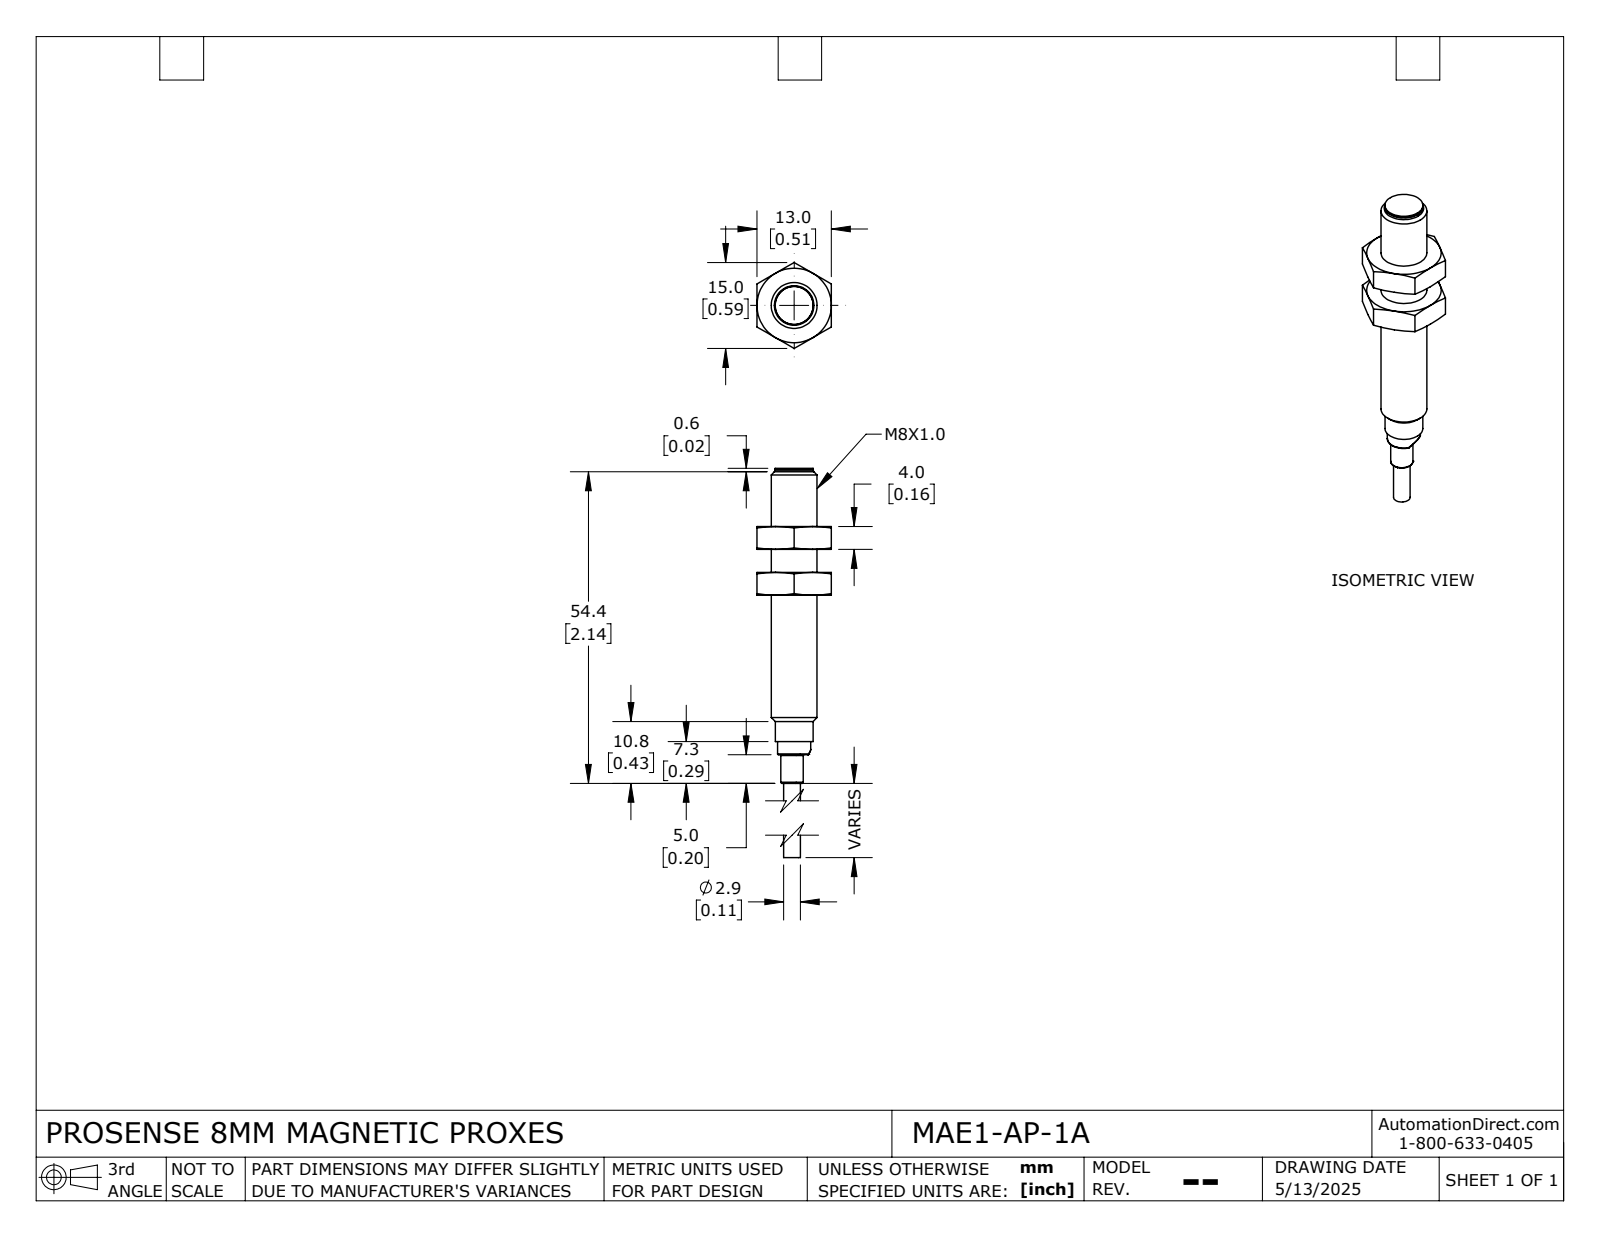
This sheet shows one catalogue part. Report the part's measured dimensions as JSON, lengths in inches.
{"part_name": "ME5020Z01", "step_written_by": "SolidWorks 2024 (AUTOMOTIVE_DESIGN)", "units": "inches", "bodies": {"solids": 6, "faces": 170, "planar": 58, "cylindrical": 42, "other": 70}, "overall_size": [2.461, 0.591, 0.512], "volume_in3": 0.13, "surface_area_in2": 5.763, "round_holes": [[0.12, 1], [0.154, 1], [0.183, 1], [0.23, 1], [0.272, 1]], "round_bosses_or_shafts": [[0.017, 3], [0.315, 1], [0.263, 1], [0.261, 1], [0.26, 1], [0.228, 1], [0.204, 1], [0.114, 1]], "partial_cylinders_radius": [[0.098, 1], [0.104, 1], [0.108, 1]], "face_to_face_distances": [0.157, 0.315, 0.511, 0.472, 0.512, 0.865, 0.707, 0.55, 0.392, 0.872], "hole_center_spacings": [0.016]}
